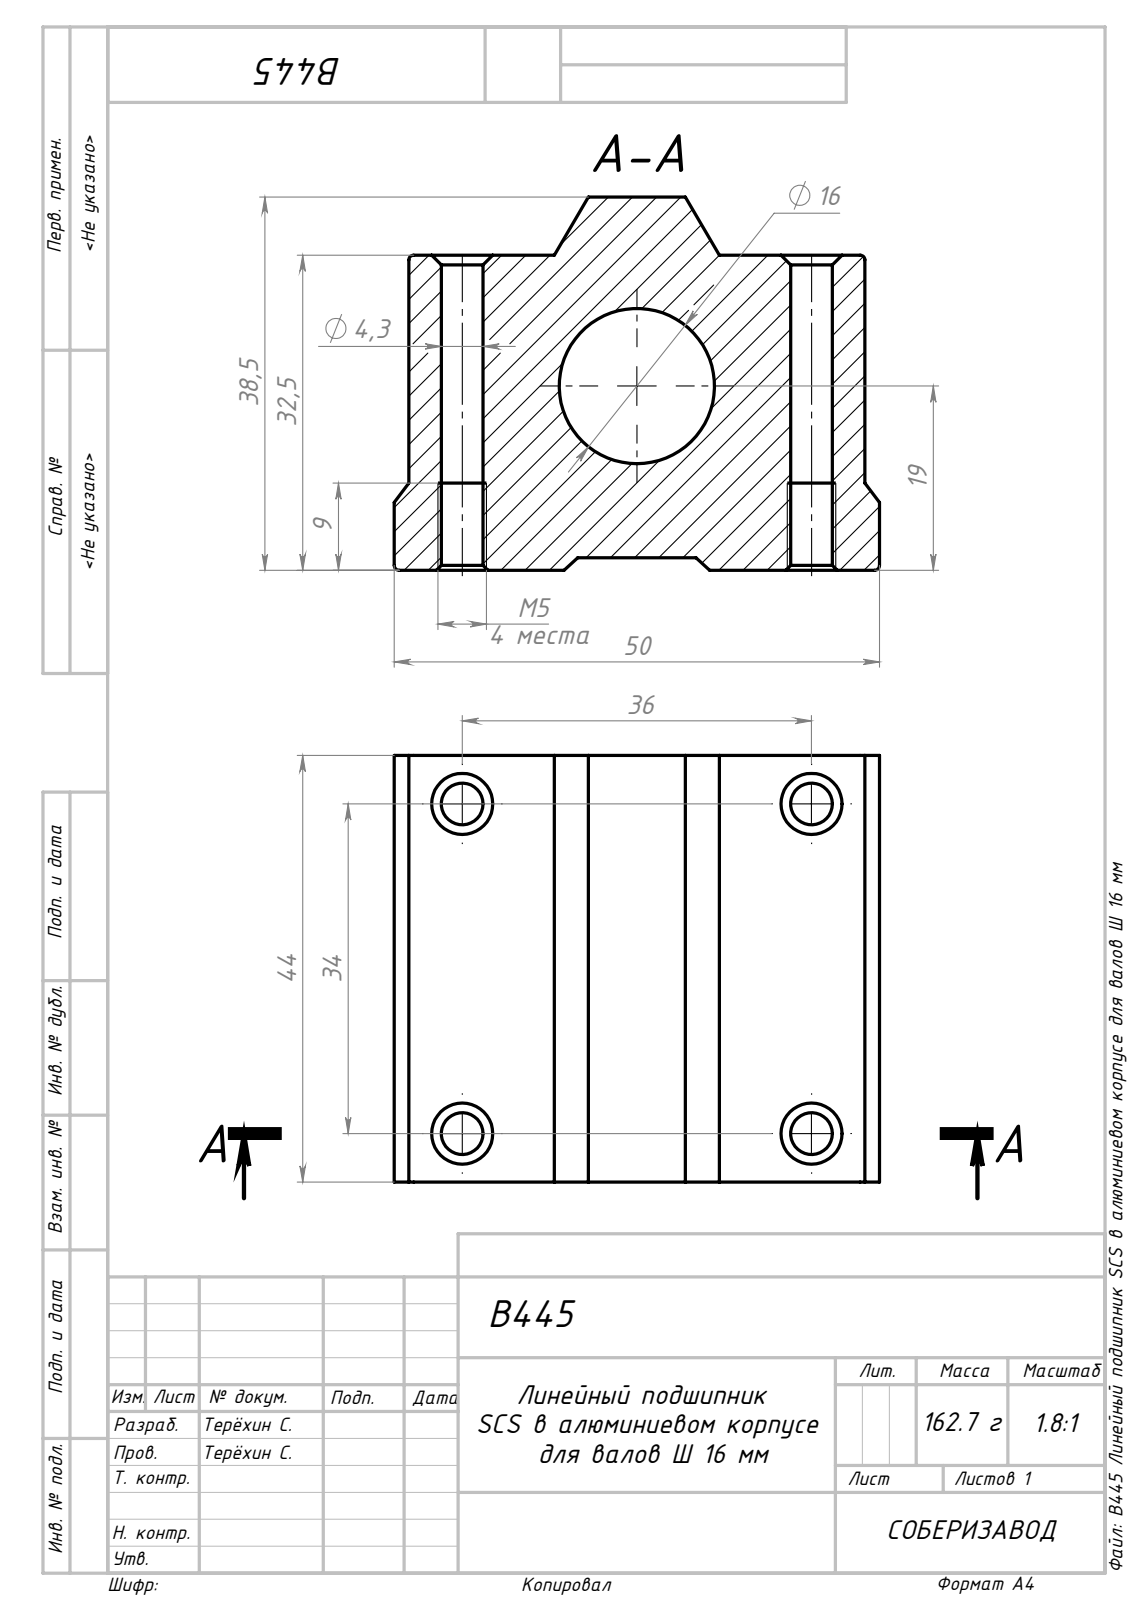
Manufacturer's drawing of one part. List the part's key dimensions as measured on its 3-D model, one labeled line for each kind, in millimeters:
Part name (STEP PRODUCT): Сборка3; B445 Линейный подшипник SCS в алюминиевом корпусе для валов Ø 16 мм_SCS16UU
STEP written by: SolidWorks 2024 (AUTOMOTIVE_DESIGN)
Units: millimetres
Bodies: 1 solid, 48 faces (18 planar, 14 cylindrical, 16 other)
Overall size (bounding box): 50 × 44 × 38.5
Volume: 60 270 mm³ · Surface area: 14 120 mm²
Round holes (diameter × count): ⌀4.3 ×4, ⌀16 ×1
Partial cylindrical surfaces — rounded edges, fillets, slot ends (radius × count): R0.5 ×4
Main face-to-face distances: 44, 32.5, 47, 1.5, 48.5, 1.3, 31.2, 38.5, 37.2, 6
Hole centre spacings: 34, 36, 49.52
